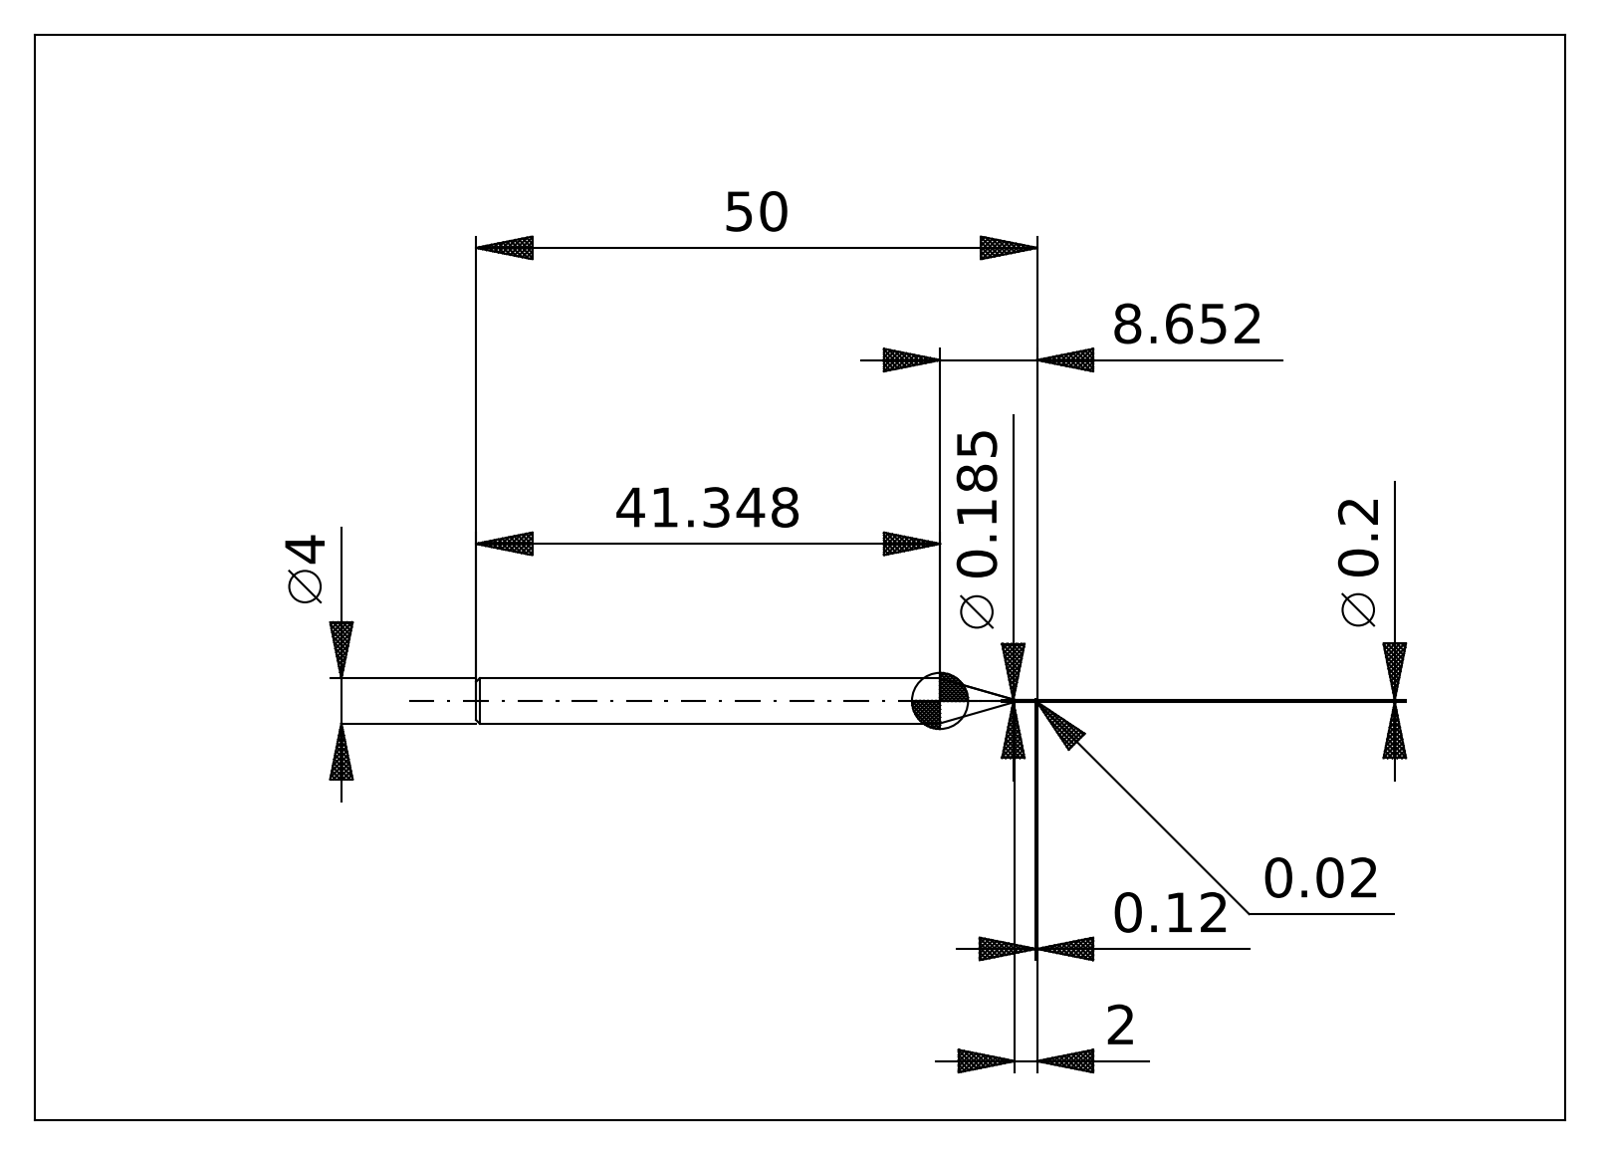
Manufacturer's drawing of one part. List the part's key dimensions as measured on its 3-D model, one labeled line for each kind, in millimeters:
STEP written by: ACIS (automotive_design)
Units: millimetres
Bodies: 2 solids, 26 faces (6 planar, 8 cylindrical, 12 other)
Overall size (bounding box): 50 × 4 × 4
Volume: 548 mm³ · Surface area: 577 mm²
Round bosses / shafts (diameter × count): ⌀4 ×1
Main face-to-face distances: 50, 49.97, 49.88, 8.65, 8.62, 8.53, 41.35
